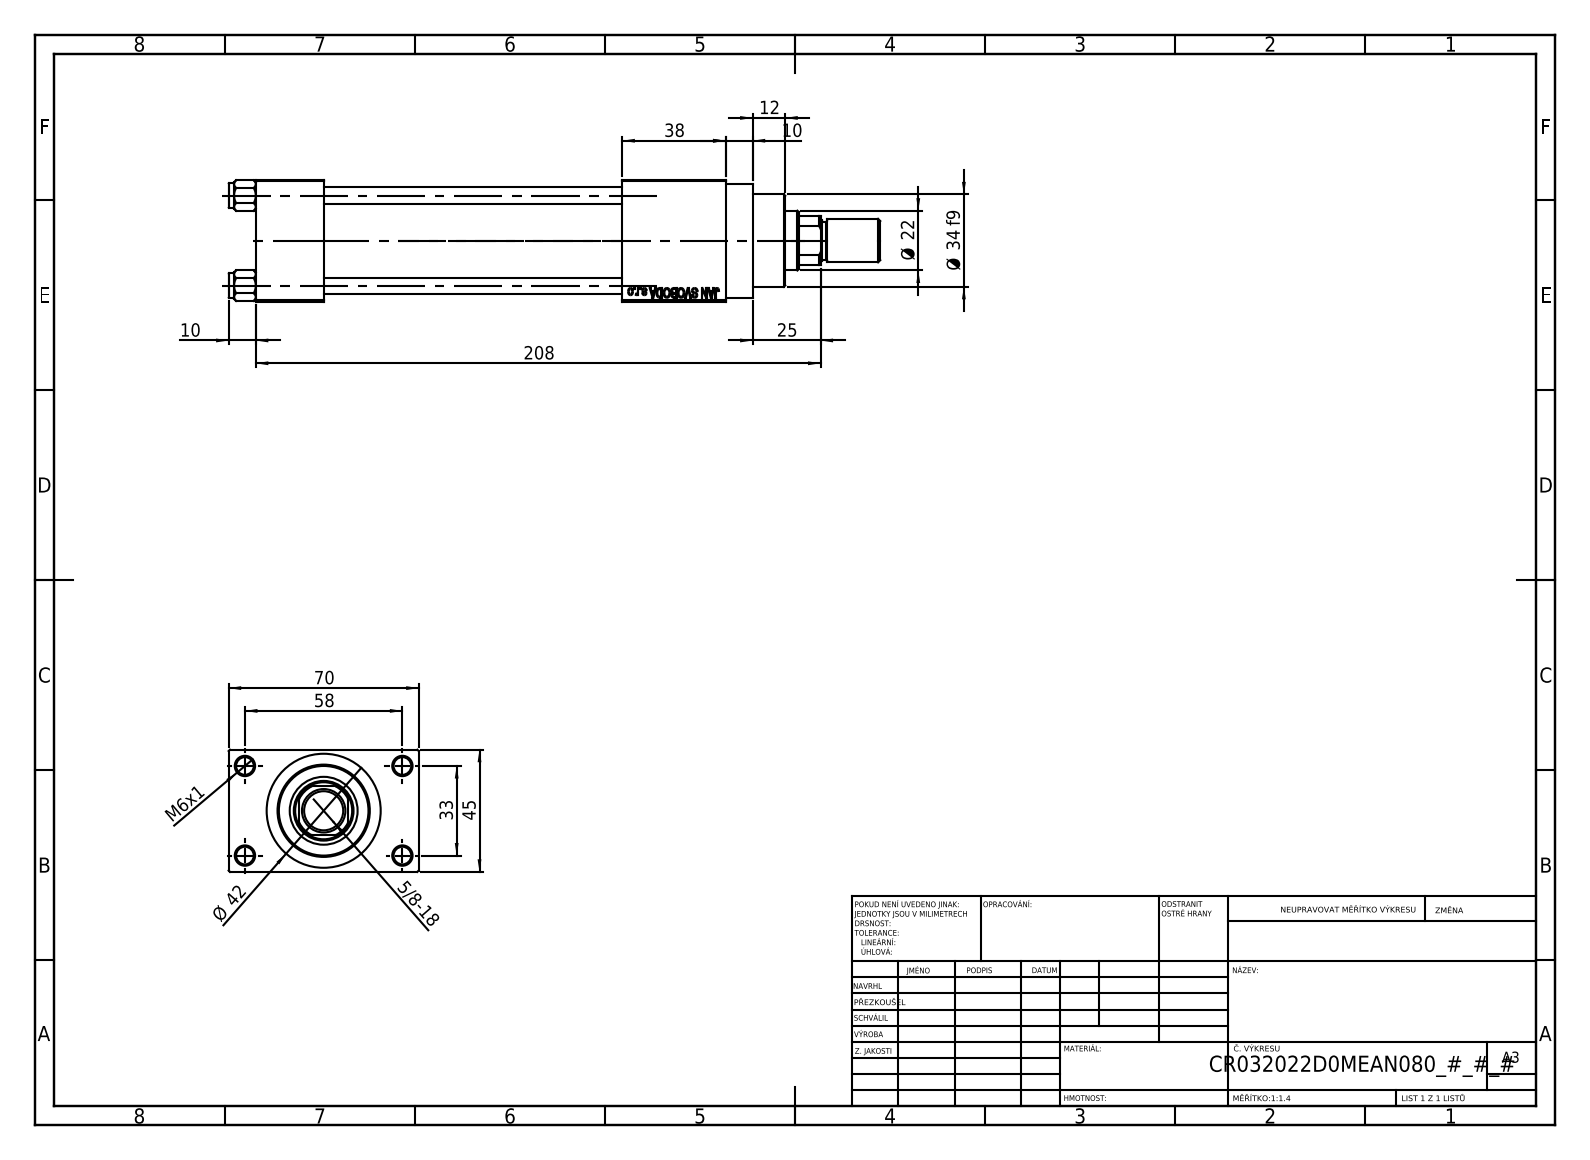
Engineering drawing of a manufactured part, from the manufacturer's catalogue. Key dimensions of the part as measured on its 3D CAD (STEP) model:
Part name (STEP PRODUCT): V215CR_VCP_D; NUT_M5_D; V215_VC_A; V215CR_D_Body (+2 more)
STEP written by: SolidWorks 2019 (CONFIG_CONTROL_DESIGN)
Units: millimetres
Bodies: 12 solids, 1117 faces (500 planar, 93 cylindrical, 524 other)
Overall size (bounding box): 240 × 70 × 45
Volume: 298 322 mm³ · Surface area: 102 860 mm²
Round holes (diameter × count): ⌀6 ×4, ⌀6.5 ×4, ⌀7 ×2, ⌀13.16 ×2, ⌀20 ×2, ⌀10.5 ×1, ⌀22 ×1, ⌀24 ×1, ⌀25 ×1, ⌀32 ×1, ⌀33 ×1
Round bosses / shafts (diameter × count): ⌀9 ×4, ⌀42 ×1, ⌀38 ×1, ⌀34 ×1, ⌀16 ×1, ⌀14 ×1
Partial cylindrical surfaces — rounded edges, fillets, slot ends (radius × count): R10.5 ×1
Main face-to-face distances: 45, 25, 12.5, 57.5, 110, 135, 148, 70, 38, 173
Hole centre spacings: 12.4, 23.48, 33.2, 33.37, 35.35, 45.6, 56.35, 33
